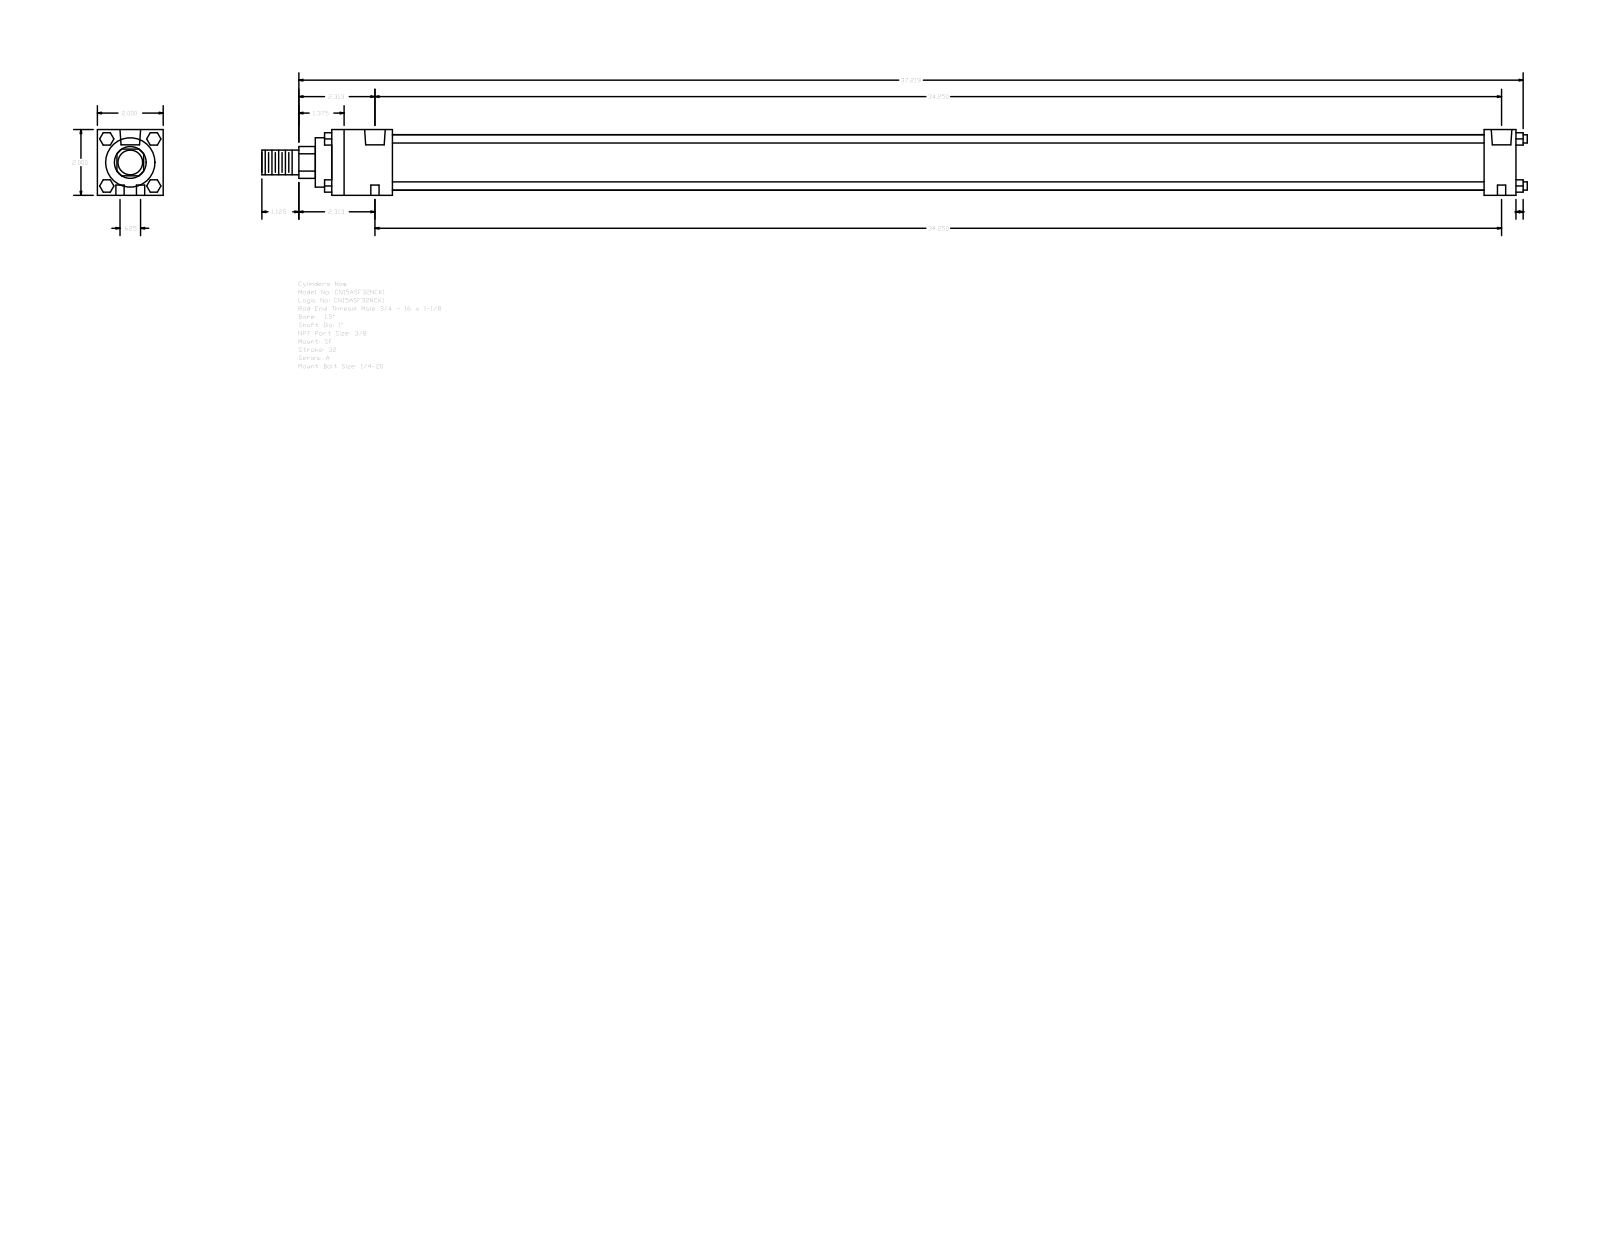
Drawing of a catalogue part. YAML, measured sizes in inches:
part_name: "A_SF__0150_1"
step_written_by: "GSSL Pune (CONFIG_CONTROL_DESIGN)"
units: inches
bodies: {solids: 0, faces: 124, planar: 94, cylindrical: 30, other: 0}
overall_size: [38.469, 2, 2]
round_holes:
  - {diameter: 0.25, count: 4}
  - {diameter: 0.219, count: 2}
  - {diameter: 0.627, count: 2}
round_bosses_or_shafts:
  - {diameter: 0.25, count: 4}
  - {diameter: 1.69, count: 1}
  - {diameter: 1.5, count: 1}
  - {diameter: 1, count: 1}
  - {diameter: 0.75, count: 1}
partial_cylinders:
  - {radius: 0.484, count: 1}
face_to_face_distances: [2, 36, 1.844, 35.031, 33.187, 34.156, 0.969, 0.5, 2.344, 35.531]
hole_center_spacings: [0.313, 34.252, 34.25, 0.625, 34.256, 33.937]
